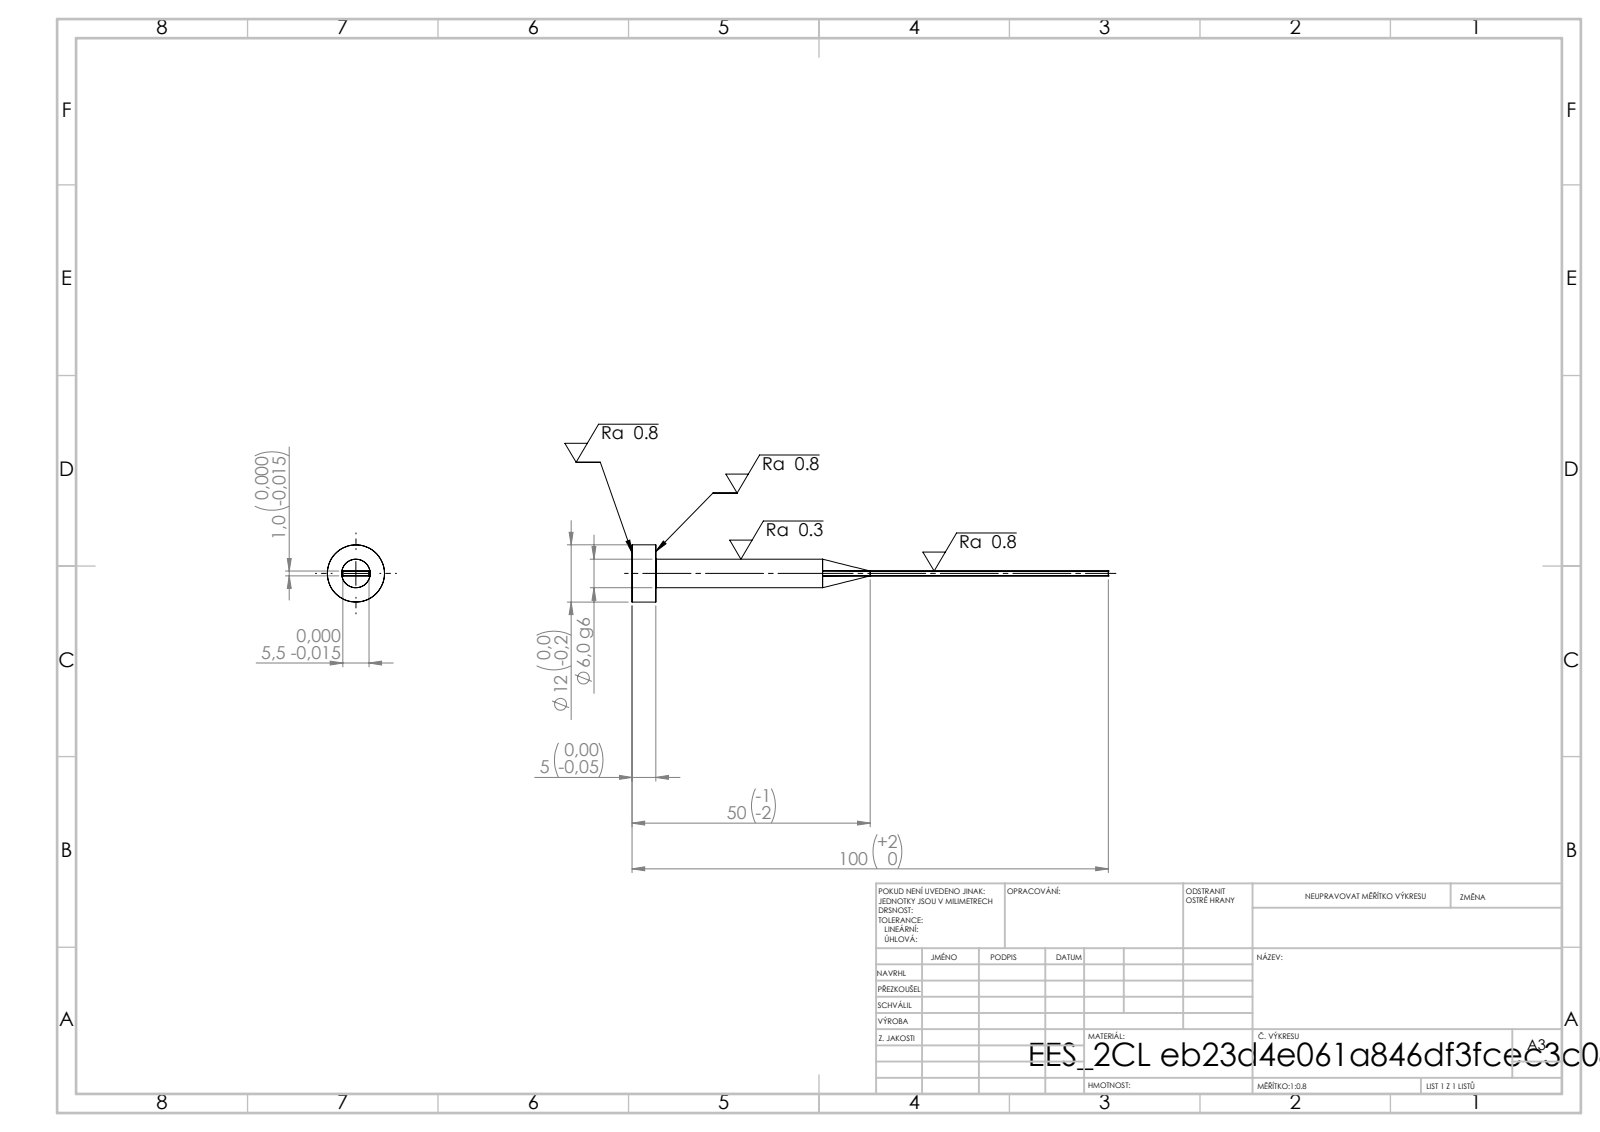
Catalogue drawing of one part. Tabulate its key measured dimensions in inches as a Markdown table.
| quantity | value |
| --- | --- |
| STEP written by | SolidWorks 2019 (CONFIG_CONTROL_DESIGN) |
| units | inches |
| bodies | 1 solid, 15 faces (7 planar, 4 cylindrical, 4 other) |
| overall size | 3.937 × 0.472 × 0.472 |
| volume | 0.121 in³ |
| surface area | 2.877 in² |
| round bosses / shafts (diameter × count) | 0.472 × 1, 0.236 × 1 |
| main face-to-face distances | 0.039, 0.197, 0.217, 3.937, 3.74 |
